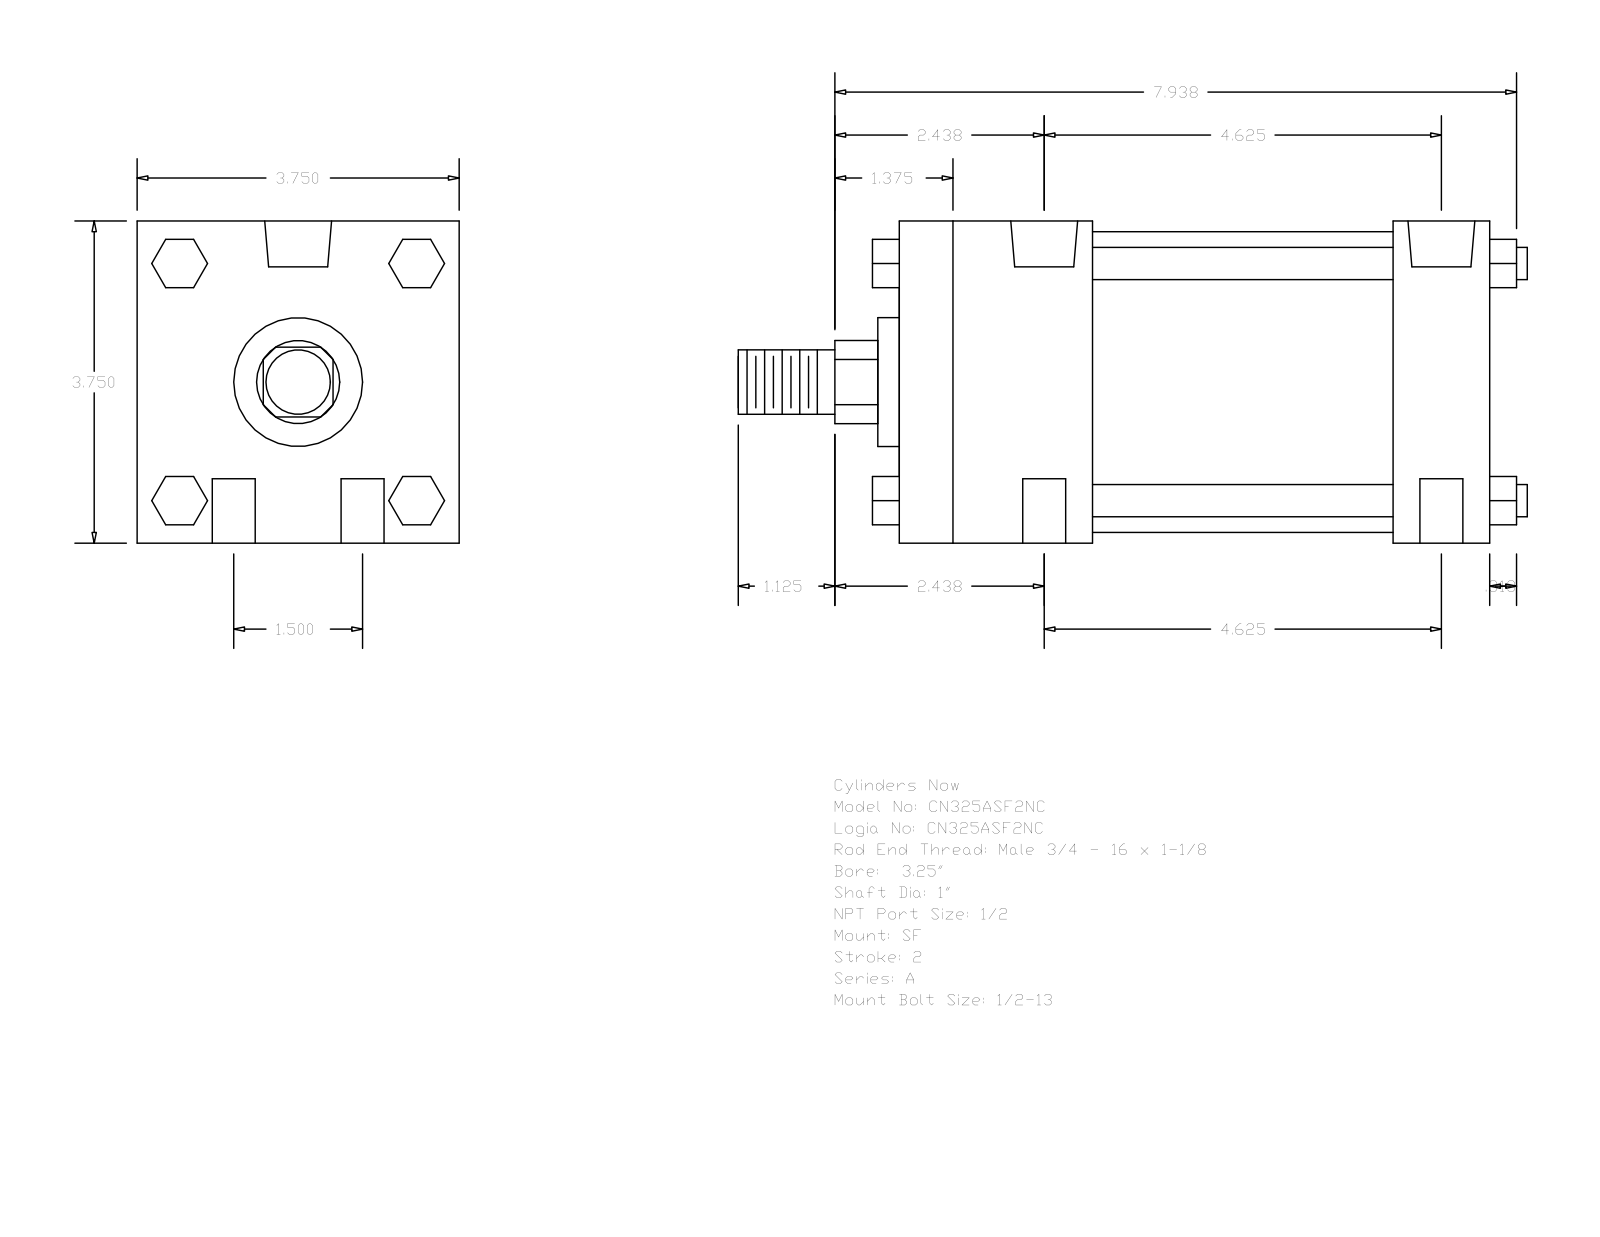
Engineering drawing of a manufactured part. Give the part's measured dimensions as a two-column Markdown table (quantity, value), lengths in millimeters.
| quantity | value |
| --- | --- |
| part name | A_SF__0325_1 |
| STEP written by | GSSL Pune (CONFIG_CONTROL_DESIGN) |
| units | millimeters |
| bodies | 0 solids, 124 faces (94 planar, 30 cylindrical, 0 other) |
| overall size | 233.36 × 95.25 × 95.25 |
| round holes (diameter × count) | 12.7 × 4, 8.73 × 2, 19.77 × 2 |
| round bosses / shafts (diameter × count) | 9.53 × 4, 88.9 × 1, 38.1 × 1, 25.4 × 1, 19.05 × 1 |
| partial cylindrical surfaces (radius × count) | 12.29 × 1 |
| main face-to-face distances | 95.24, 174.63, 146.05, 28.58, 57.15, 88.9, 117.48, 14.28, 35.05, 60.71 |
| hole center spacings | 19.05, 119.01, 117.48, 38.1, 123.5, 111.12 |
